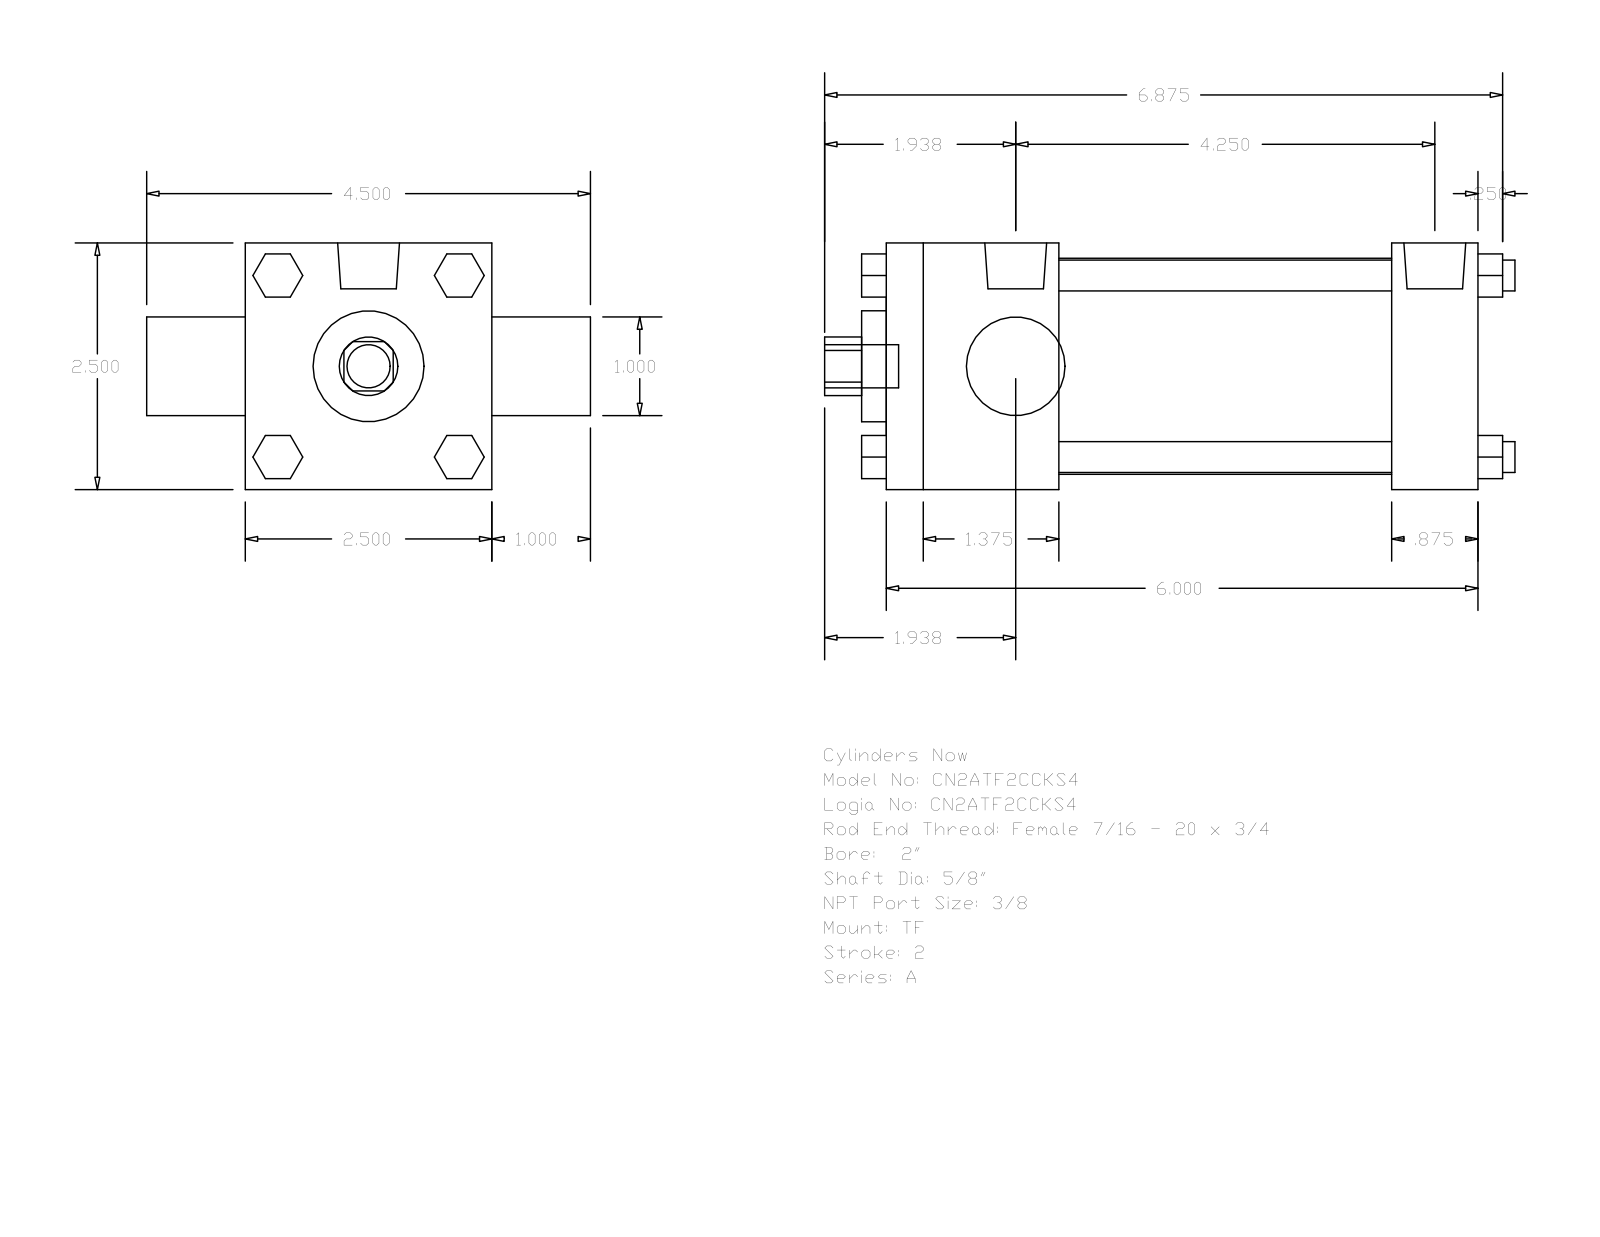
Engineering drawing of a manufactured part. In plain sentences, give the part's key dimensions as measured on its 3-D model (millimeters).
The part is named "A_TF__0200_0.625". Its 3-D file was written by "GSSL Pune (CONFIG_CONTROL_DESIGN)". It is 0 solids with 120 faces: 92 planar, 28 cylindrical and 0 other. Overall it measures 177.8 by 114.3 by 63.5 millimeters. Round holes: 1 of diameter 15.88, 1 of diameter 25.4, 1 of diameter 28.57, 1 of diameter 55.63. Round bosses or shafts: 4 of diameter 7.94, 3 of diameter 5.56, 2 of diameter 15.93, 1 of diameter 11.11. Partial cylindrical surfaces (rounded edges, fillets, slot ends): 1 of radius 7.54. The main face-to-face distances are 63.5, 152.4, 44.45, 130.17, 85.72, 107.95, 22.23, 25.4, 88.9, 50.8.
